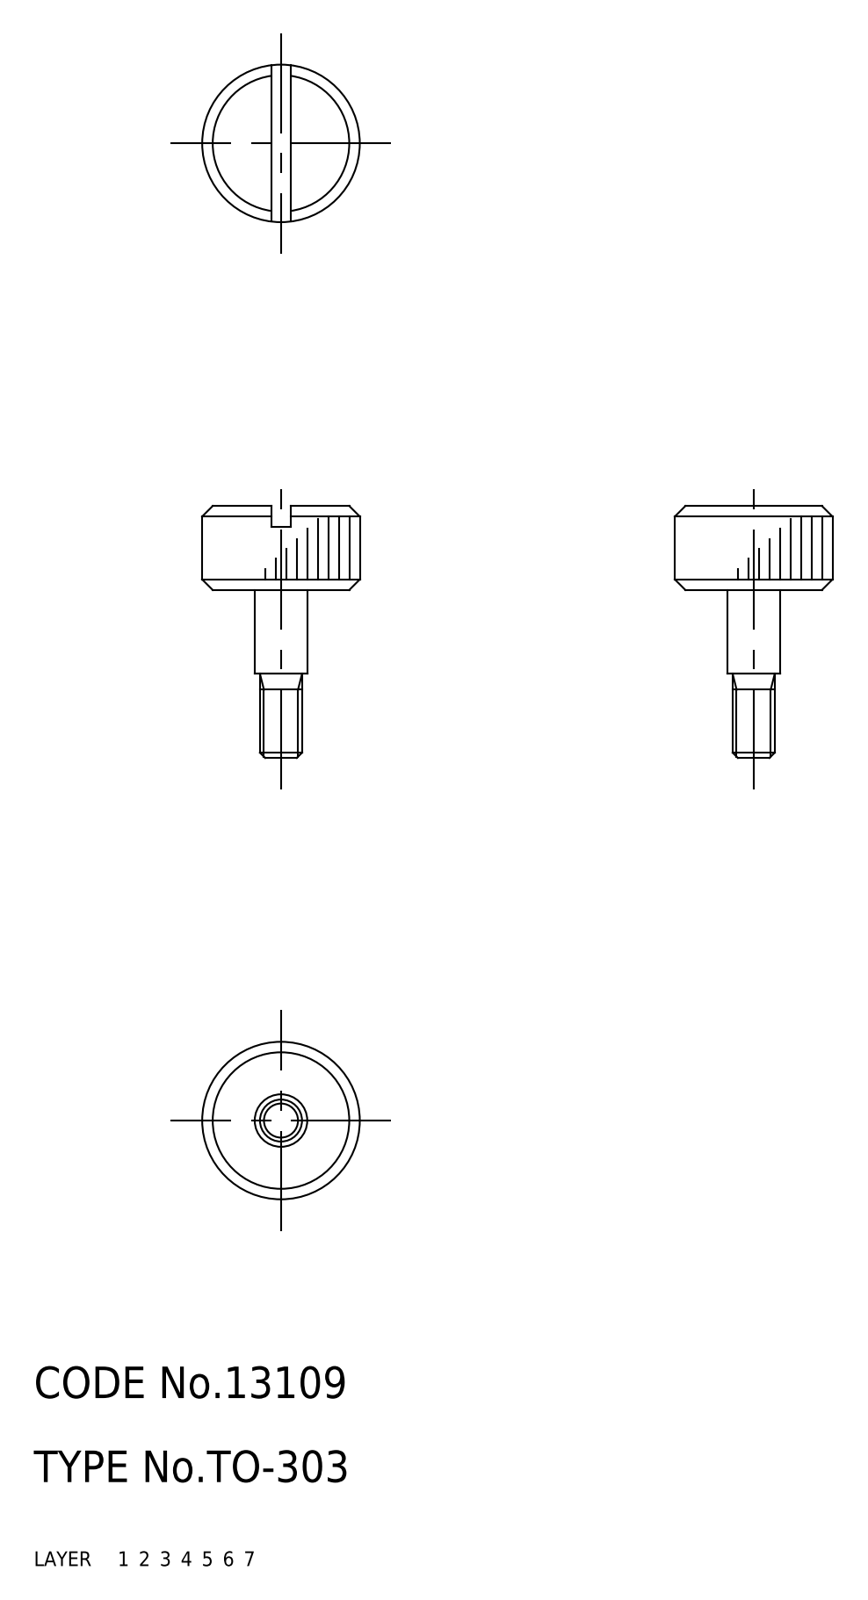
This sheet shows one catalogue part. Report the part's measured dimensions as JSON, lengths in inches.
{"part_name": "67110055", "step_written_by": "CADfix (AUTOMOTIVE_DESIGN)", "units": "inches", "bodies": {"solids": 1, "faces": 20, "planar": 0, "cylindrical": 0, "other": 20}, "overall_size": [0.945, 0.591, 0.591], "volume_in3": 0.096, "surface_area_in2": 1.47}
